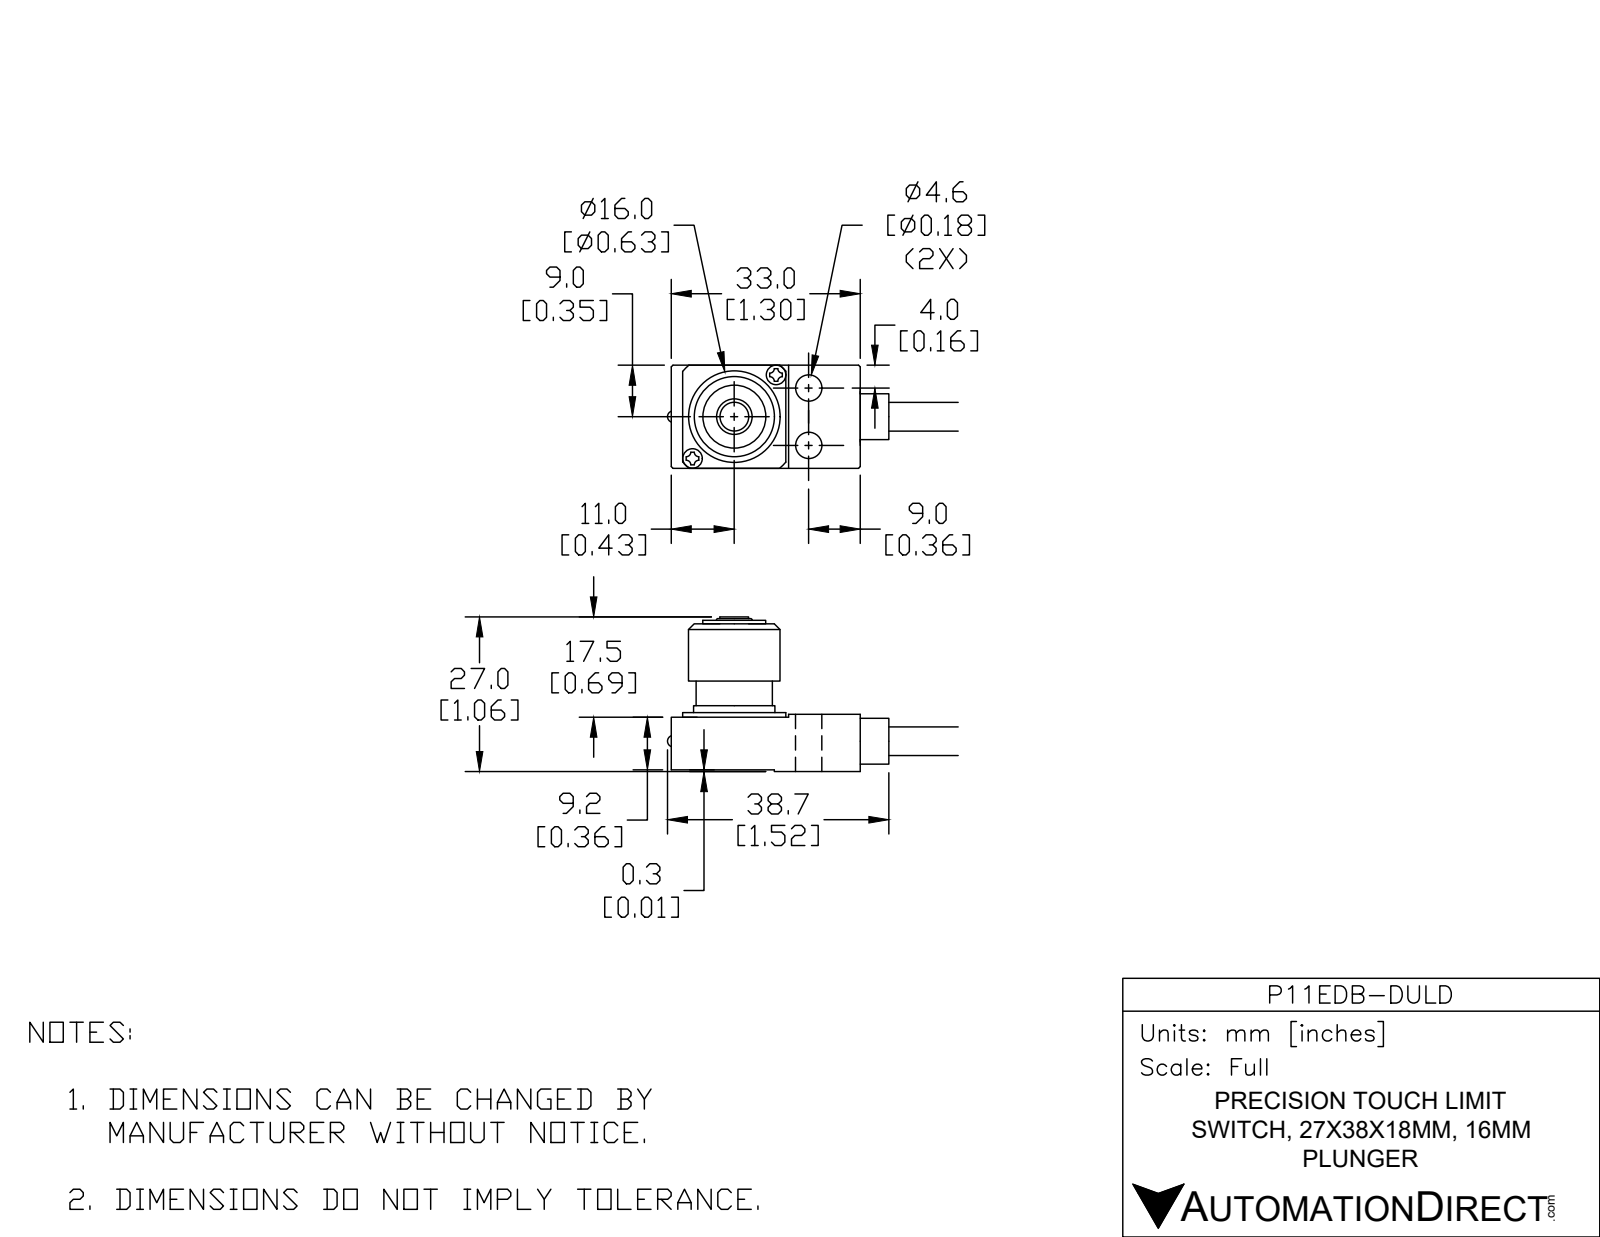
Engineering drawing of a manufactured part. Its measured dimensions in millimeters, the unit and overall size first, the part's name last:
Units: millimetres
Overall size (bounding box): 46.16 × 25 × 18
Round holes (diameter × count): ⌀3.2 ×2, ⌀4.6 ×2
Round bosses / shafts (diameter × count): ⌀5 ×2, ⌀3 ×2, ⌀16 ×1, ⌀14.2 ×1, ⌀13.3 ×1, ⌀11 ×1, ⌀8 ×1, ⌀6.2 ×1
Partial cylindrical surfaces — rounded edges, fillets, slot ends (radius × count): R12 ×1
Main face-to-face distances: 10, 18, 9.7, 10.3, 13.5, 33, 13.8, 0.6, 24.4, 14.4
Hole centre spacings: 6.15, 10, 13.56, 20.43, 20.65, 23.74
Volume: 8 527 mm³ · Surface area: 3 577 mm²
Bodies: 1 solid, 108 faces (40 planar, 51 cylindrical, 17 other)
Part name (STEP PRODUCT): P11EDB-DULD
STEP written by: SolidWorks 2017 (CONFIG_CONTROL_DESIGN)
